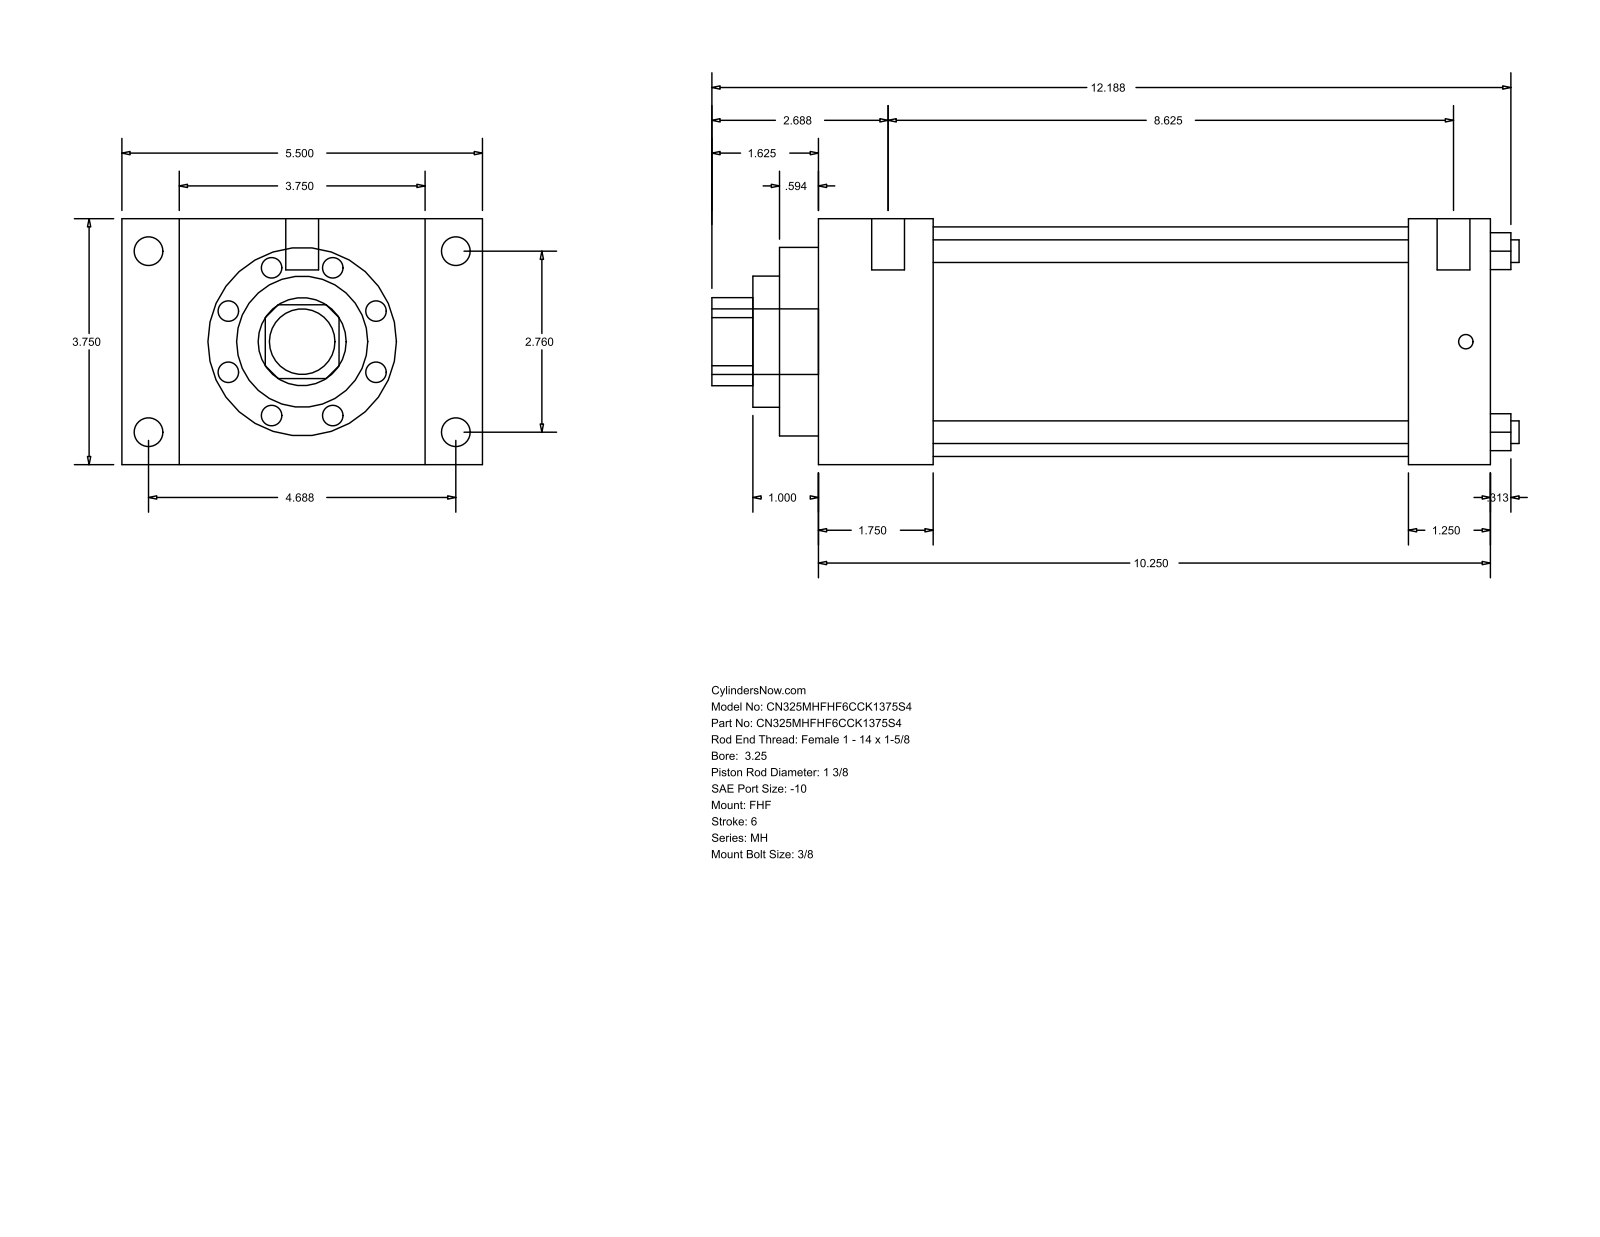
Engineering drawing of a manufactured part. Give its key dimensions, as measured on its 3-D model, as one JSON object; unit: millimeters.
{"part_name": "MH_FHF__0325_1.375", "step_written_by": "GSSL Pune (CONFIG_CONTROL_DESIGN)", "units": "millimeters", "bodies": {"solids": 0, "faces": 90, "planar": 61, "cylindrical": 29, "other": 0}, "overall_size": [312.74, 139.7, 95.25], "round_holes": [[8.76, 4], [34.92, 1], [50.8, 1], [73.03, 1], [88.9, 1]], "round_bosses_or_shafts": [[11.13, 4], [5.56, 4], [12.7, 2], [25.4, 1]], "partial_cylinders_radius": [[17.06, 1]], "face_to_face_distances": [95.24, 260.35, 44.45, 215.9, 22.23, 117.47, 139.7, 228.61, 184.16, 31.74], "hole_center_spacings": [49.57, 70.1, 99.14]}
